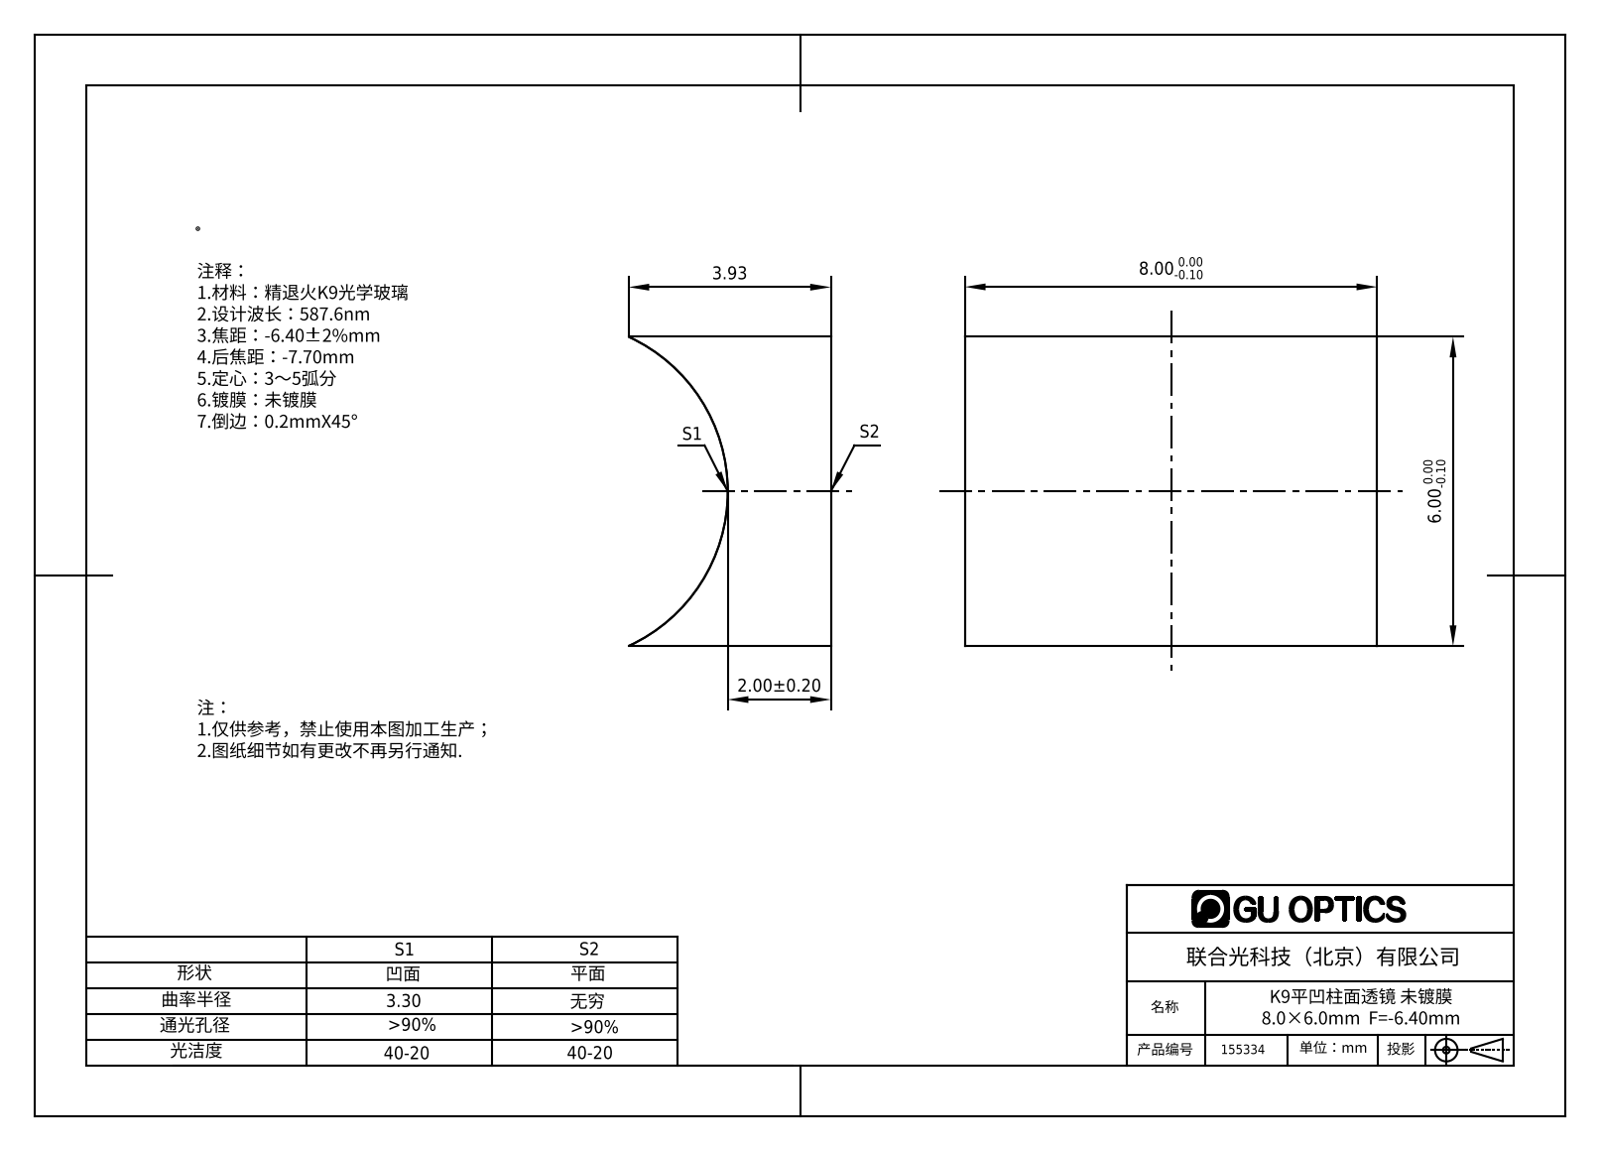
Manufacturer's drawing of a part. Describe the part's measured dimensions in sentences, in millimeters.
The part is named "155334". Its 3-D file was written by "SolidWorks 2016 (AUTOMOTIVE_DESIGN)". It is 1 solid with 6 faces: 5 planar, 1 cylindrical and 0 other. Overall it measures 8 by 6 by 3.92 millimeters. Its volume is 122 cubic millimeters and its surface area 202 square millimeters. Partial cylindrical surfaces (rounded edges, fillets, slot ends): 1 of radius 3.3. The main face-to-face distances are 6, 8.
